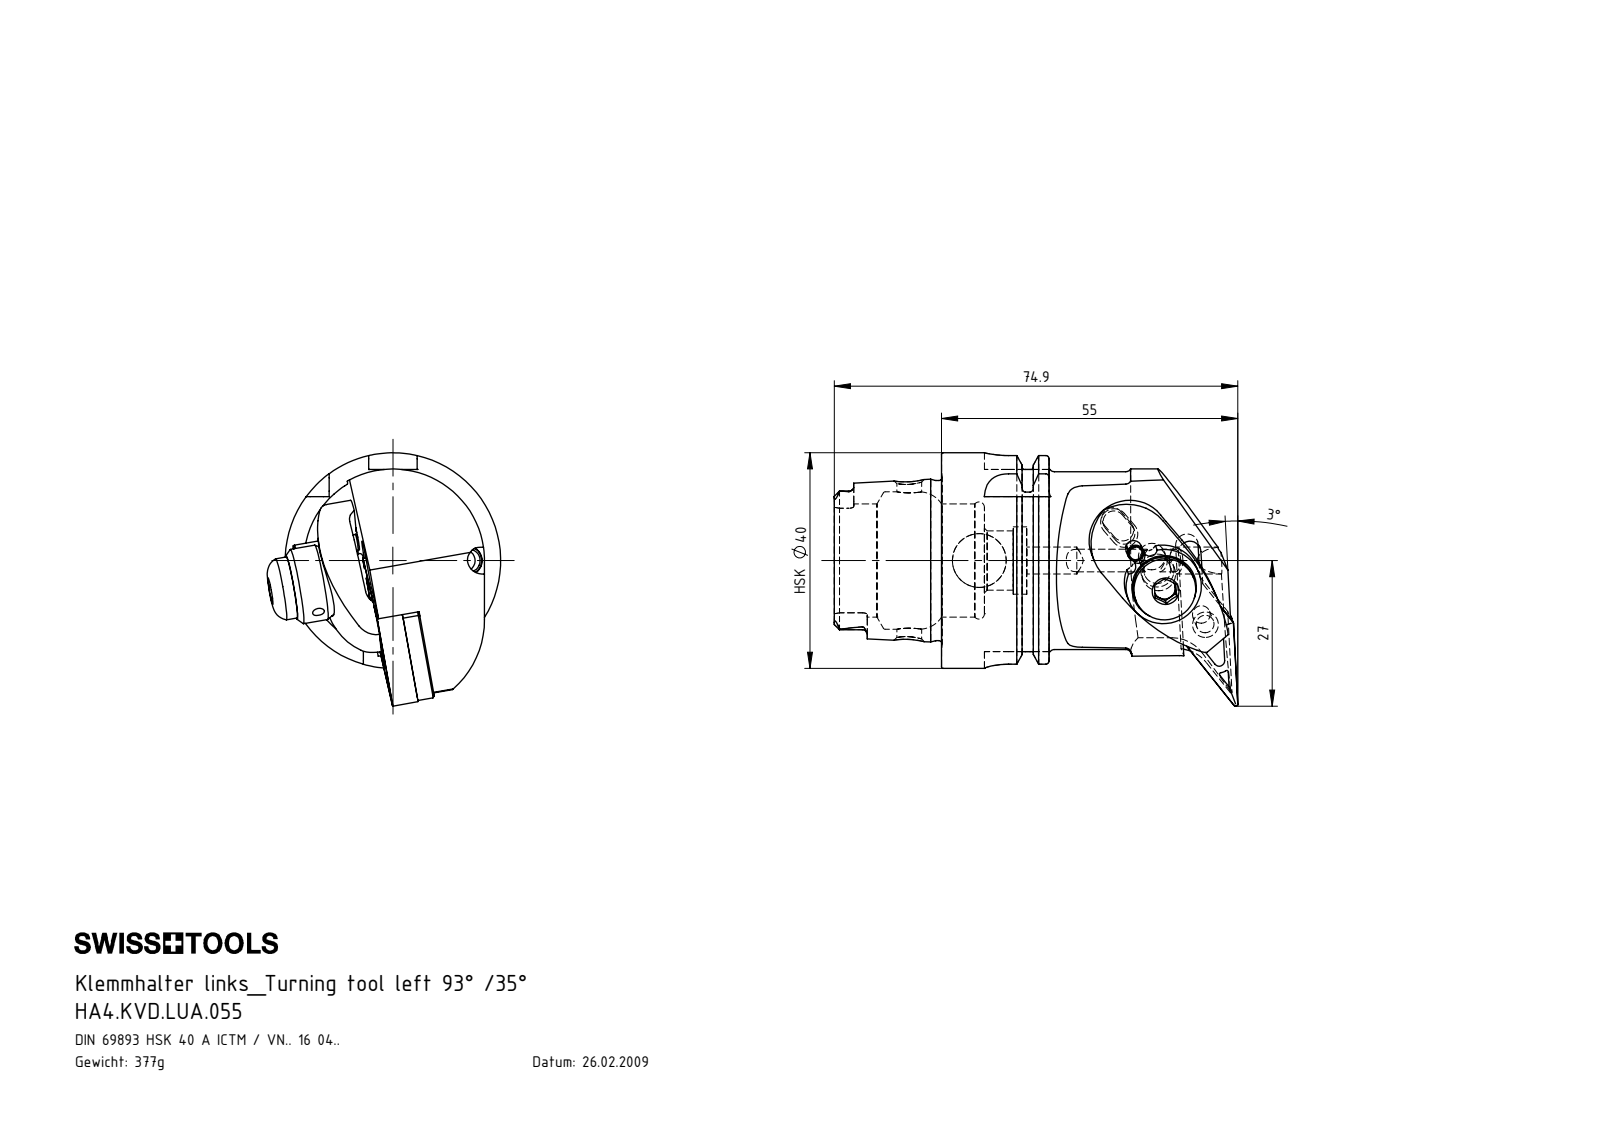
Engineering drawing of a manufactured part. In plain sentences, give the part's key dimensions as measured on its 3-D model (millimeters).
The part is named "WCC-ER5.102.005_A; WCC-ER5.102.012_B; WVD-ER2.101.003_A; HA4.KVD.LUA.055 (+7 more)". Its 3-D file was written by "SolidWorks 2017 (AUTOMOTIVE_DESIGN)". It is 11 solids with 467 faces: 126 planar, 154 cylindrical and 187 other. Overall it measures 74.9 by 47 by 43.33 millimeters. Its volume is 47 492 cubic millimeters and its surface area 18 953 square millimeters. Round holes: 3 of diameter 2, 2 of diameter 5, 2 of diameter 7, 1 of diameter 2.4, 1 of diameter 3, 1 of diameter 3.3, 1 of diameter 3.8, 1 of diameter 4, 1 of diameter 4.2, 1 of diameter 4.6, 1 of diameter 4.95, 1 of diameter 6.2. Round bosses or shafts: 2 of diameter 5, 2 of diameter 3, 1 of diameter 40, 1 of diameter 34.75, 1 of diameter 33, 1 of diameter 29.71, 1 of diameter 14, 1 of diameter 11.5. Partial cylindrical surfaces (rounded edges, fillets, slot ends): 6 of radius 0.39, 6 of radius 0.9, 4 of radius 0.4, 4 of radius 4.5, 3 of radius 0.69, 3 of radius 0.69, 3 of radius 1.5, 3 of radius 3. The main face-to-face distances are 9.04, 7.64, 7.95, 8.93, 1.29, 12, 4.46, 19.95, 9.53, 3.17. The hole center spacings are 8.02, 22.32, 14.3, 8.2, 14.12, 14.13, 14.31.
